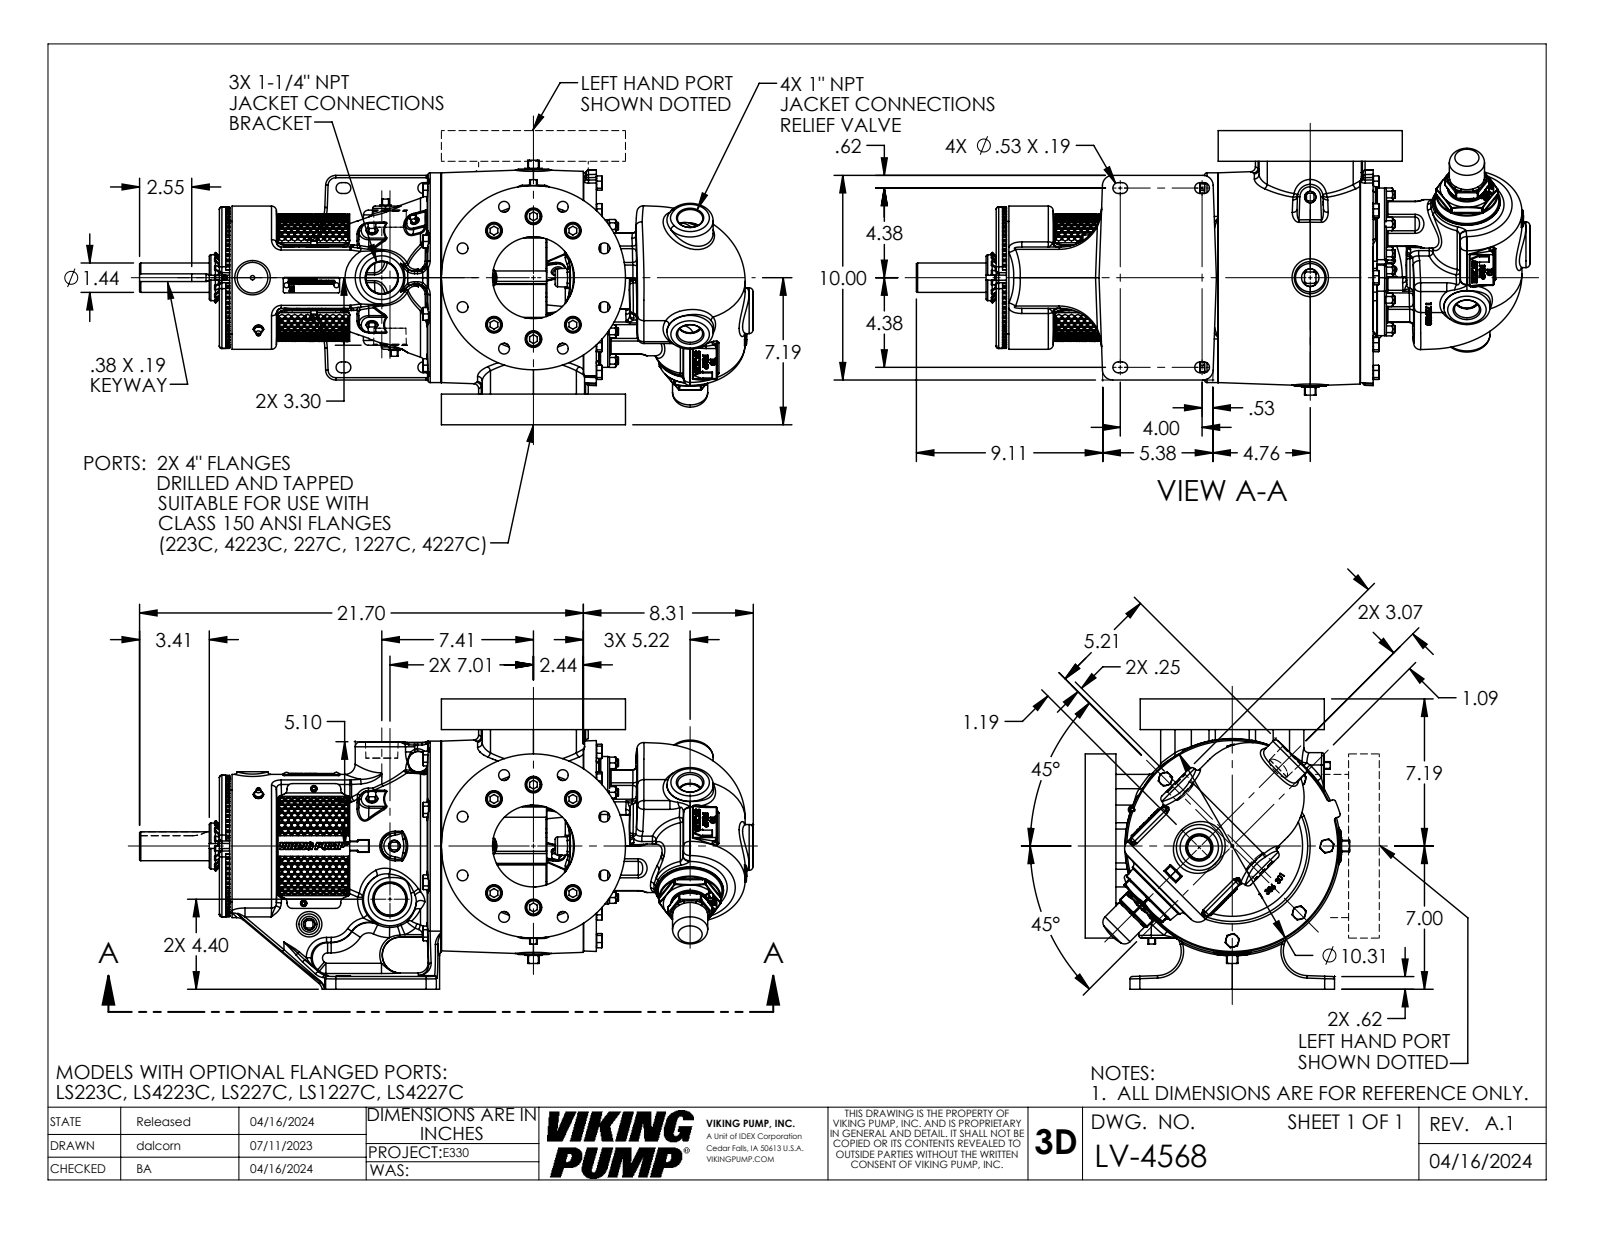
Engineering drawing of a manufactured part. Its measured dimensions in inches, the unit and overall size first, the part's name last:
Units: inches
Overall size (bounding box): 29.994 × 14.188 × 12.863
Round holes (diameter × count): ⌀0.531 ×16, ⌀0.563 ×12, ⌀0.812 ×12, ⌀1.094 ×8, ⌀0.199 ×6, ⌀0.25 ×6, ⌀0.159 ×3, ⌀0.266 ×2, ⌀0.313 ×2, ⌀0.375 ×2, ⌀4 ×2, ⌀0.453 ×1
Round bosses / shafts (diameter × count): ⌀0.75 ×12, ⌀0.5 ×12, ⌀0.625 ×10, ⌀0.369 ×8, ⌀0.625 ×6, ⌀3.5 ×3, ⌀0.437 ×3, ⌀0.312 ×3
Partial cylindrical surfaces — rounded edges, fillets, slot ends (radius × count): R0.063 ×109, R0.01 ×98, R0.12 ×88, R0.069 ×74, R0.03 ×36, R0.5 ×36, R0.24 ×16, R1 ×16
Main face-to-face distances: 14.187, 1.01, 0.49, 1.5, 13.178, 2.25, 15.669, 0.5, 3.541, 12.128
Hole centre spacings: 3, 2.87, 3.75, 5.303, 6.929, 1.375, 1.267, 1.508
Volume: 1 423 in³ · Surface area: 1 787 in²
Bodies: 1 solid, 6315 faces (1906 planar, 1133 cylindrical, 3276 other)
Part name (STEP PRODUCT): LV-4568
STEP written by: SolidWorks 2024 (AUTOMOTIVE_DESIGN)
